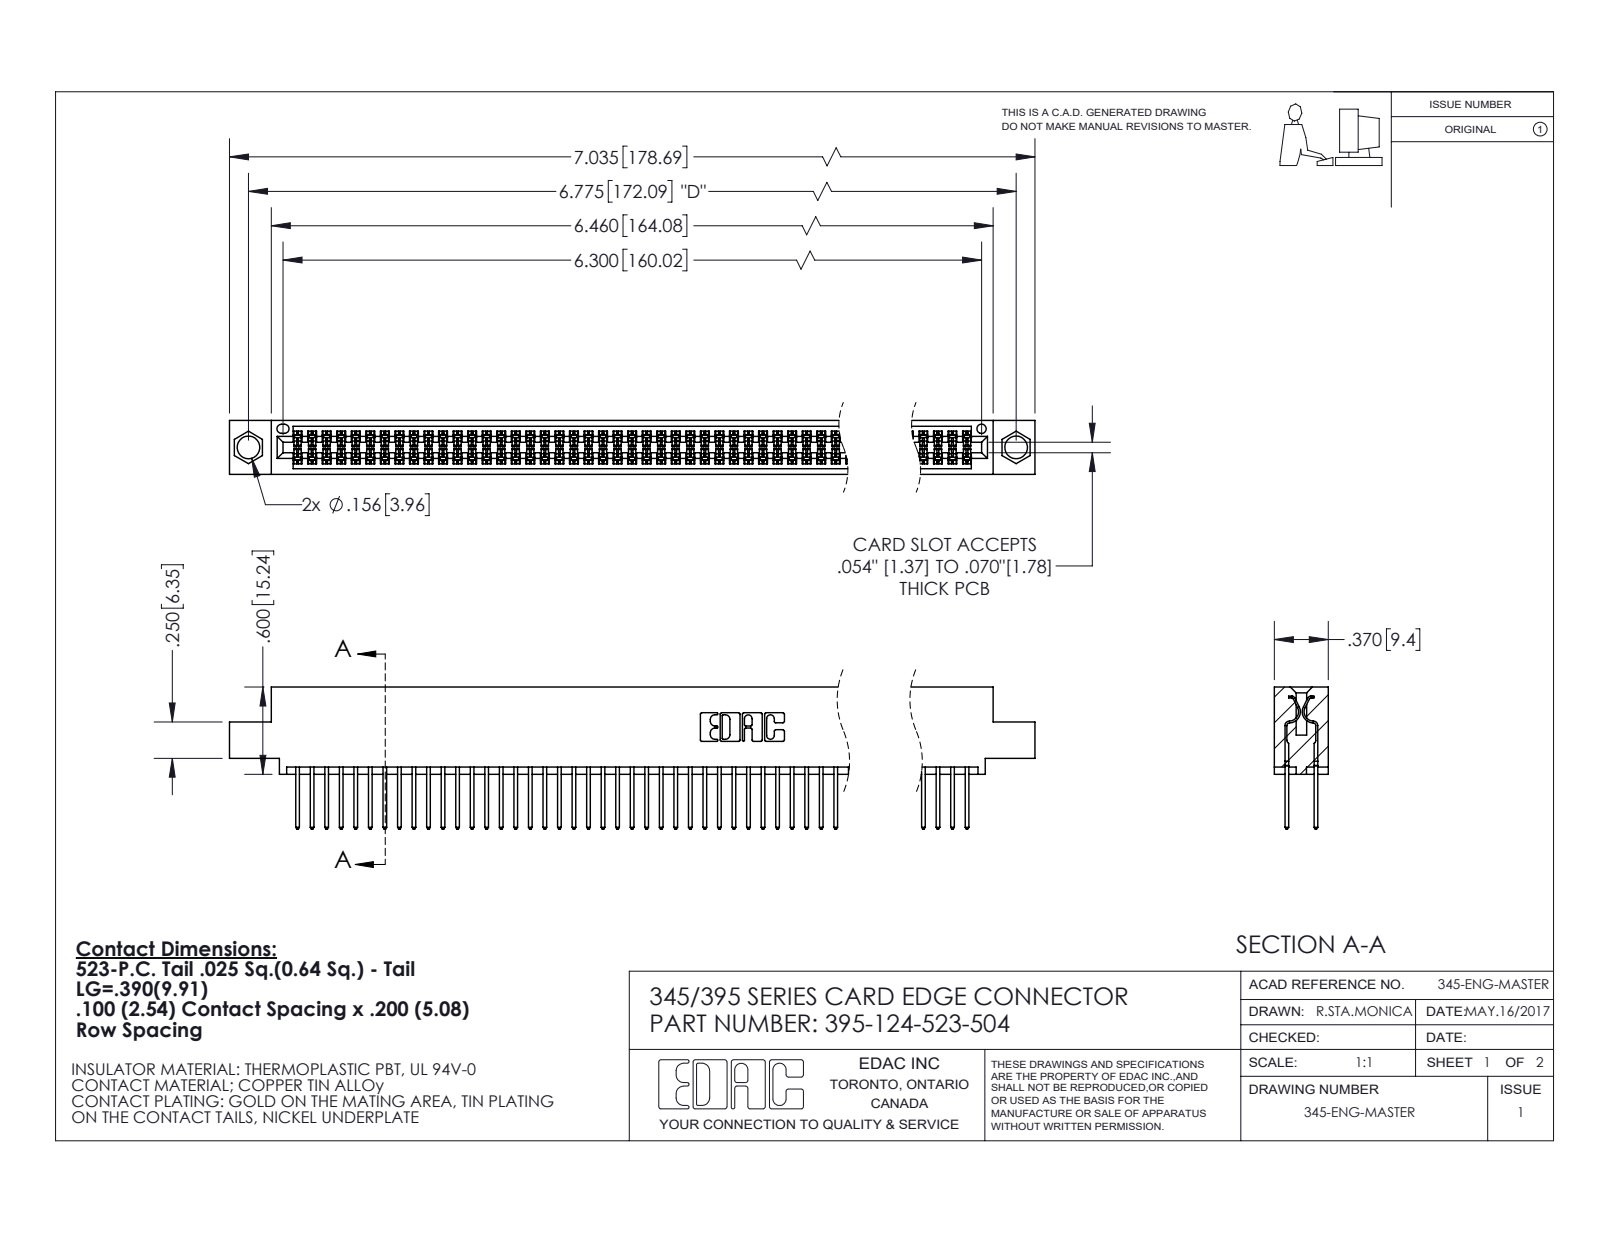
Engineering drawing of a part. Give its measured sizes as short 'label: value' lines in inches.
name: 345 Part_0.110 Offset - 0.156 Dia-TI; 395-124-523-504; 345-292-001_345-293-123
written by: SolidWorks 2020 (CONFIG_CONTROL_DESIGN)
unit: in
bodies: 125 solids, 6344 faces (4190 planar, 2154 cylindrical, 0 other)
size: 7.035 × 0.977 × 0.37
volume: 1.075 in³; area: 42.65 in²
holes: 2× ⌀0.156, 1× ⌀0.064
rounds: 186× R0.006, 124× R0.01, 22× R0.01, 6× R0.007, 6× R0.031, 3× R0.026, 2× R0.014, 2× R0.019
face distances: 0.298, 0.072, 0.2, 0.098, 0.272, 0.025, 0.37, 0.225, 0.175, 0.149
hole spacings: 0.27, 6.539, 6.775
